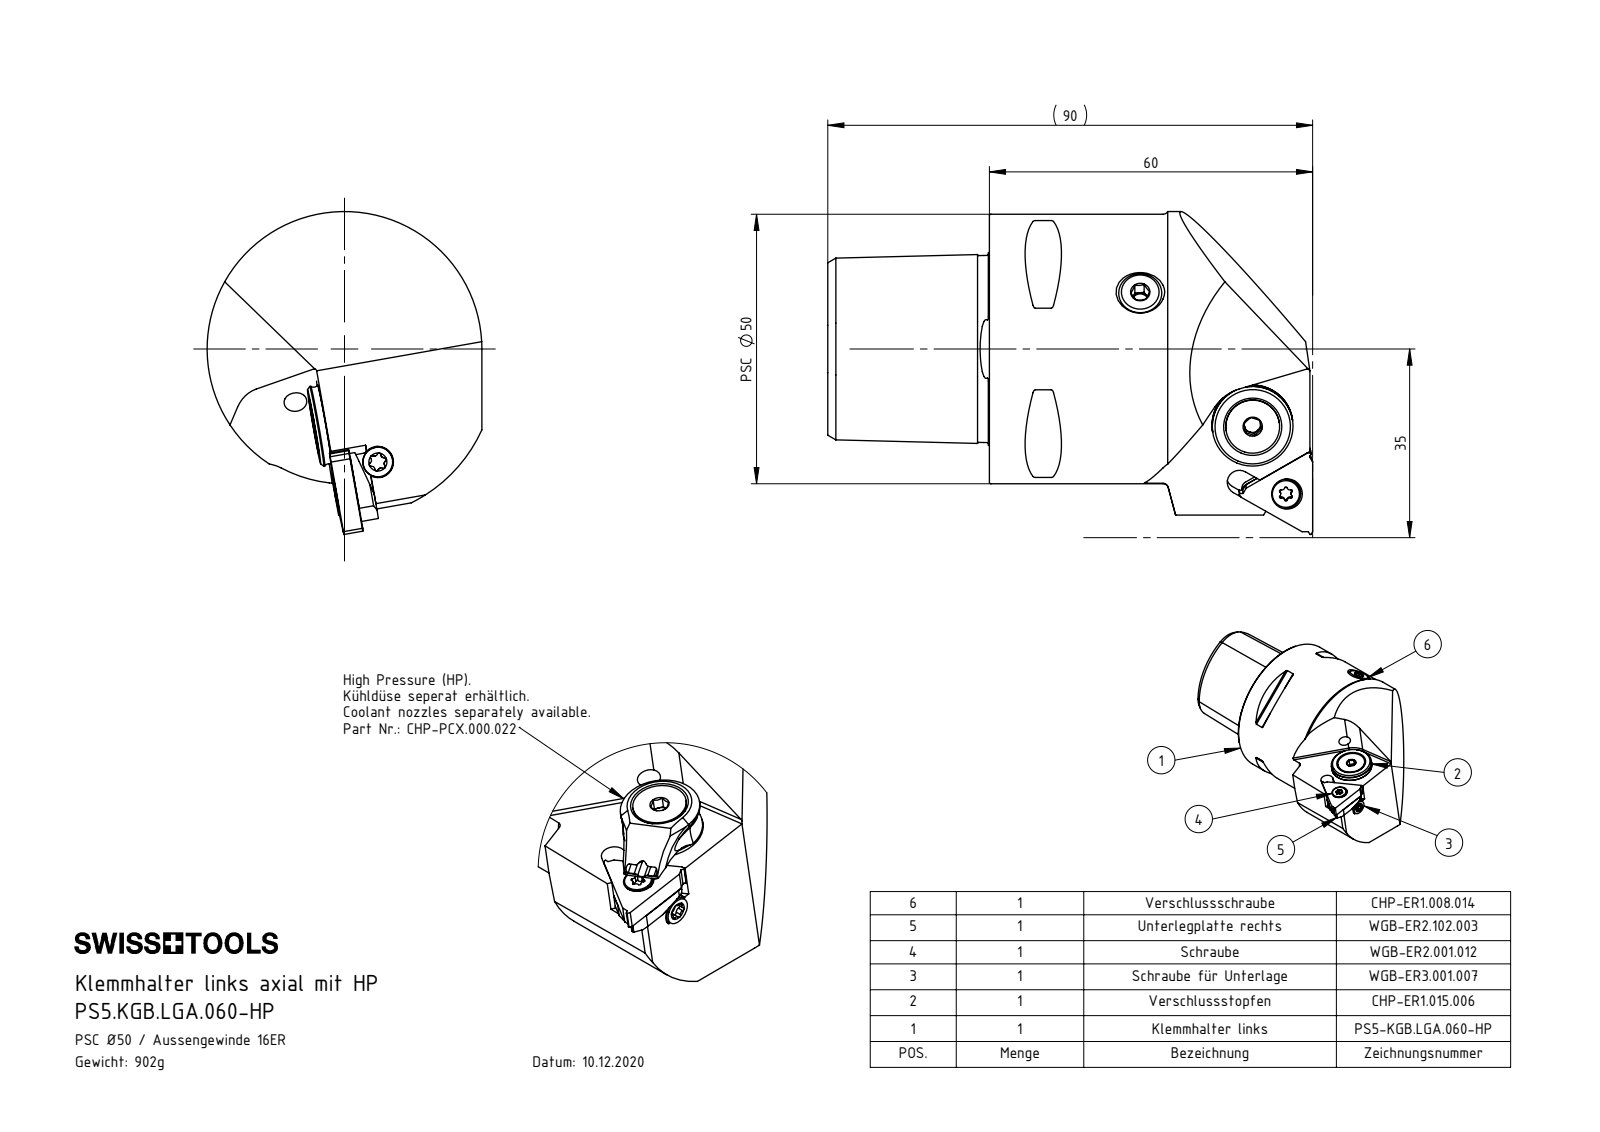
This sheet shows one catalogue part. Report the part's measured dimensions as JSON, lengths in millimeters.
{"part_name": "LT16ER; WGB-ER2.102.003_A; CHP-ER1.015.006; DIN 3771 - 13x1 (+8 more)", "step_written_by": "SolidWorks 2017 (AUTOMOTIVE_DESIGN)", "units": "millimeters", "bodies": {"solids": 10, "faces": 310, "planar": 126, "cylindrical": 84, "other": 100}, "overall_size": [90, 59.91, 51], "volume_mm3": 115013, "surface_area_mm2": 23818, "round_holes": [[4.2, 3], [2.58, 2], [4, 2], [1.2, 1], [1.6, 1], [2, 1], [2.5, 1], [3, 1], [4.02, 1], [5, 1], [5.2, 1], [6.1, 1]], "round_bosses_or_shafts": [[5.5, 3], [50, 1], [15, 1], [13.4, 1], [10, 1], [8, 1], [5, 1], [3.18, 1]], "partial_cylinders_radius": [[0.5, 10], [0.23, 6], [0.34, 6], [0.57, 6], [0.57, 6], [0.1, 2], [0.25, 1], [1.3, 1]], "face_to_face_distances": [30, 4.79, 19.18, 1.74, 6.53, 44.4, 3.65, 10, 20, 3.2], "hole_center_spacings": [4.51, 4.5, 4.53, 13.44, 13.47, 13.54, 13.56, 16.87]}
